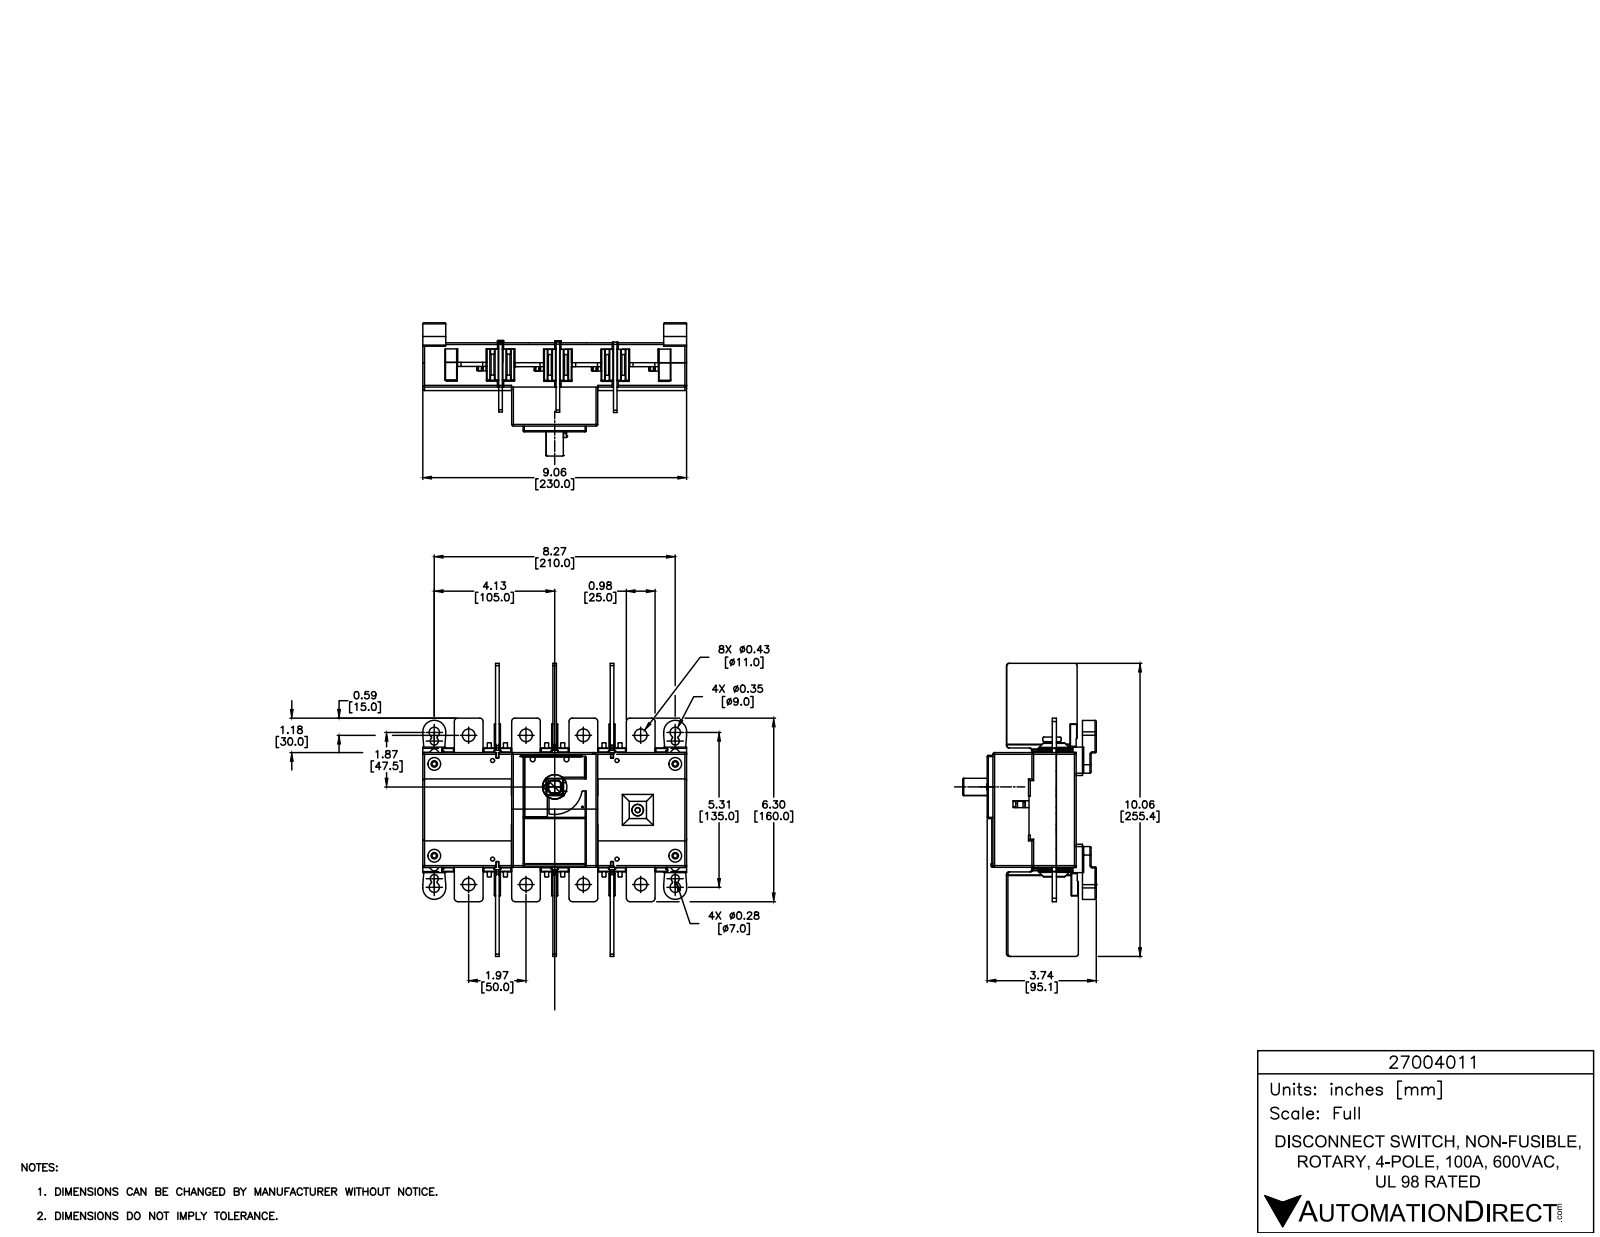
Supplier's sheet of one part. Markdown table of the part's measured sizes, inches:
| quantity | value |
| --- | --- |
| part name | 27004011 |
| STEP written by | SolidWorks 2015 (AUTOMOTIVE_DESIGN) |
| units | inches |
| bodies | 1 solid, 888 faces (562 planar, 232 cylindrical, 94 other) |
| overall size | 10.213 × 9.055 × 4.575 |
| volume | 81.86 in³ |
| surface area | 304.7 in² |
| round holes (diameter × count) | 0.433 × 12, 0.378 × 5, 0.217 × 4, 0.354 × 4, 0.165 × 1, 0.833 × 1 |
| round bosses / shafts (diameter × count) | 0.142 × 2 |
| partial cylindrical surfaces (radius × count) | 0.039 × 48, 0.079 × 20, 0.138 × 4, 0.315 × 4, 0.394 × 4, 0.02 × 1, 0.15 × 1, 0.236 × 1 |
| main face-to-face distances | 1.969, 0.122, 3.937, 2.091, 1.846, 0.819, 4.059, 3.815, 1.52, 3.051 |
| hole center spacings | 1.969, 2.178, 4.744, 3.937, 5.605, 0.931, 4.046, 4.317 |
